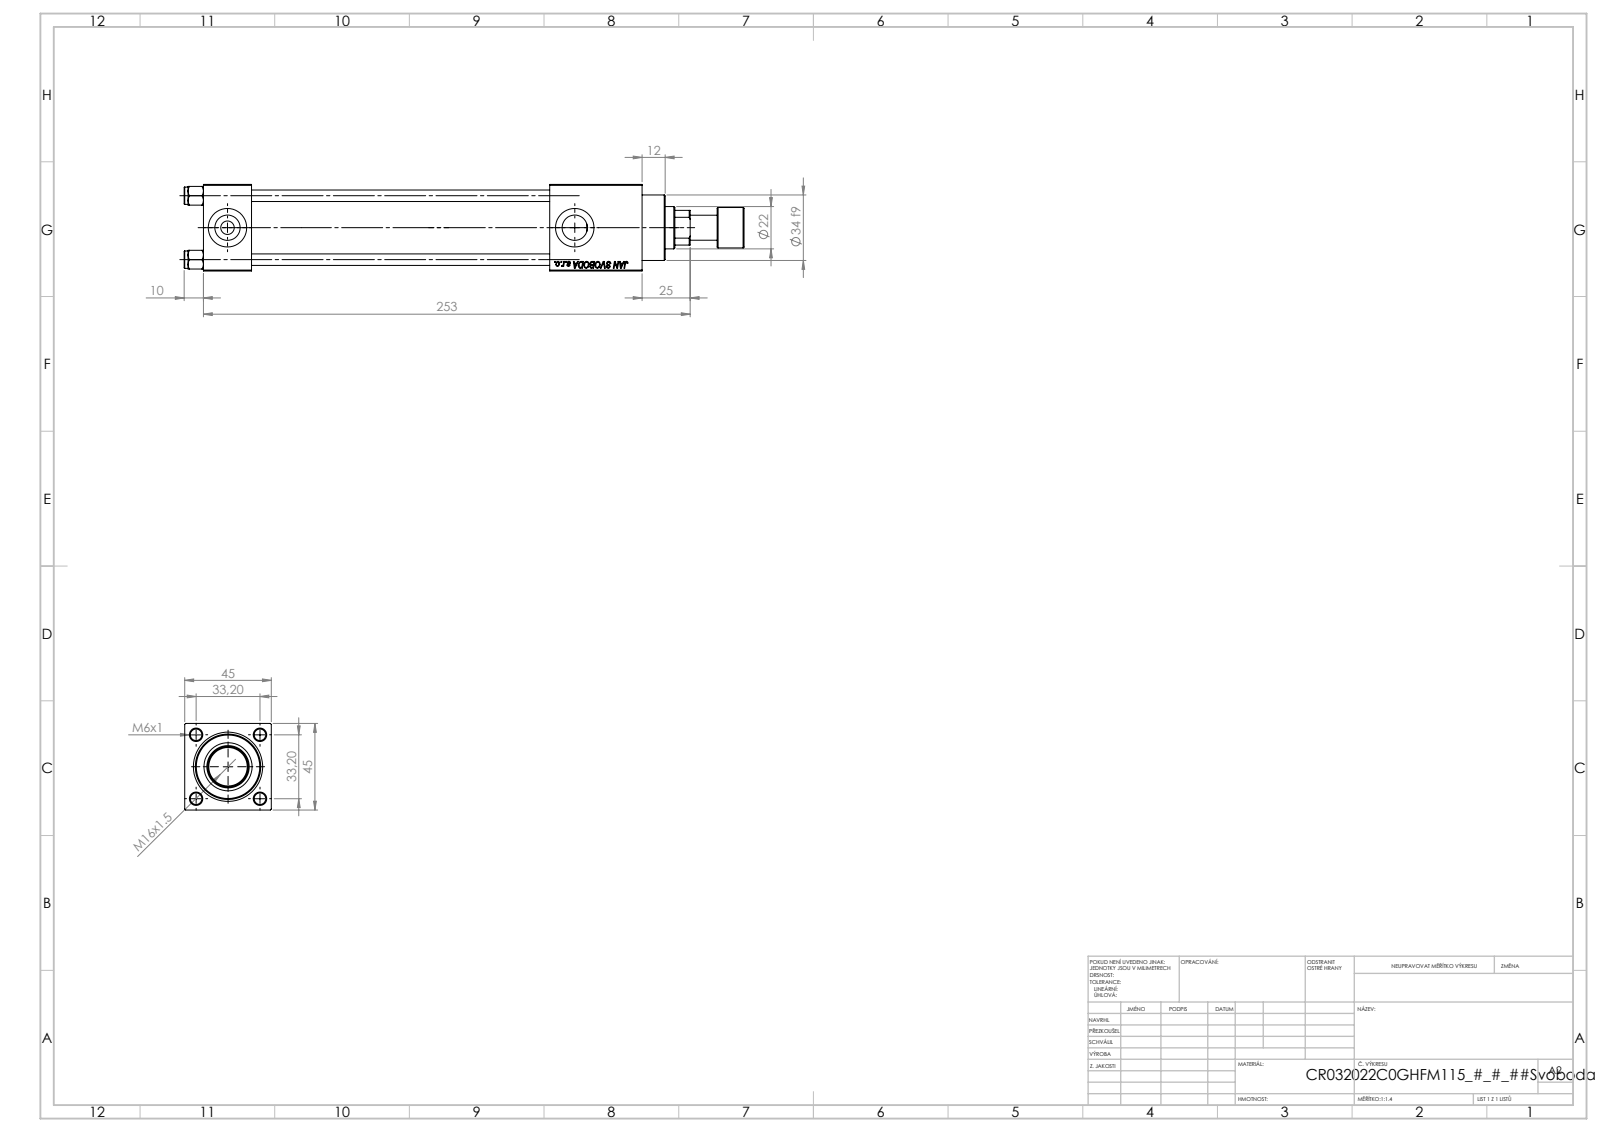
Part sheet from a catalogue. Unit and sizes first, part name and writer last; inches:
Units: inches
Overall size (bounding box): 11.457 × 1.772 × 1.772
Round holes (diameter × count): ⌀0.236 ×4, ⌀0.276 ×2, ⌀0.518 ×2, ⌀0.787 ×2, ⌀0.413 ×1, ⌀0.866 ×1, ⌀0.945 ×1, ⌀0.984 ×1, ⌀1.26 ×1, ⌀1.299 ×1
Round bosses / shafts (diameter × count): ⌀0.354 ×4, ⌀1.496 ×1, ⌀1.339 ×1, ⌀0.827 ×1, ⌀0.512 ×1
Main face-to-face distances: 1.772, 0.984, 8.976, 7.087, 6.102, 7.992, 1.89, 7.846, 6.862, 0.76
Hole centre spacings: 0.924, 1.307, 1.848, 7.106
Volume: 18.49 in³ · Surface area: 173.2 in²
Bodies: 12 solids, 1158 faces (528 planar, 90 cylindrical, 540 other)
Part name (STEP PRODUCT): V215_VC_A; V215CR_VCP_C; V215CR_C_TYCINKA; NUT_M5_C (+2 more)
STEP written by: SolidWorks 2019 (CONFIG_CONTROL_DESIGN)
